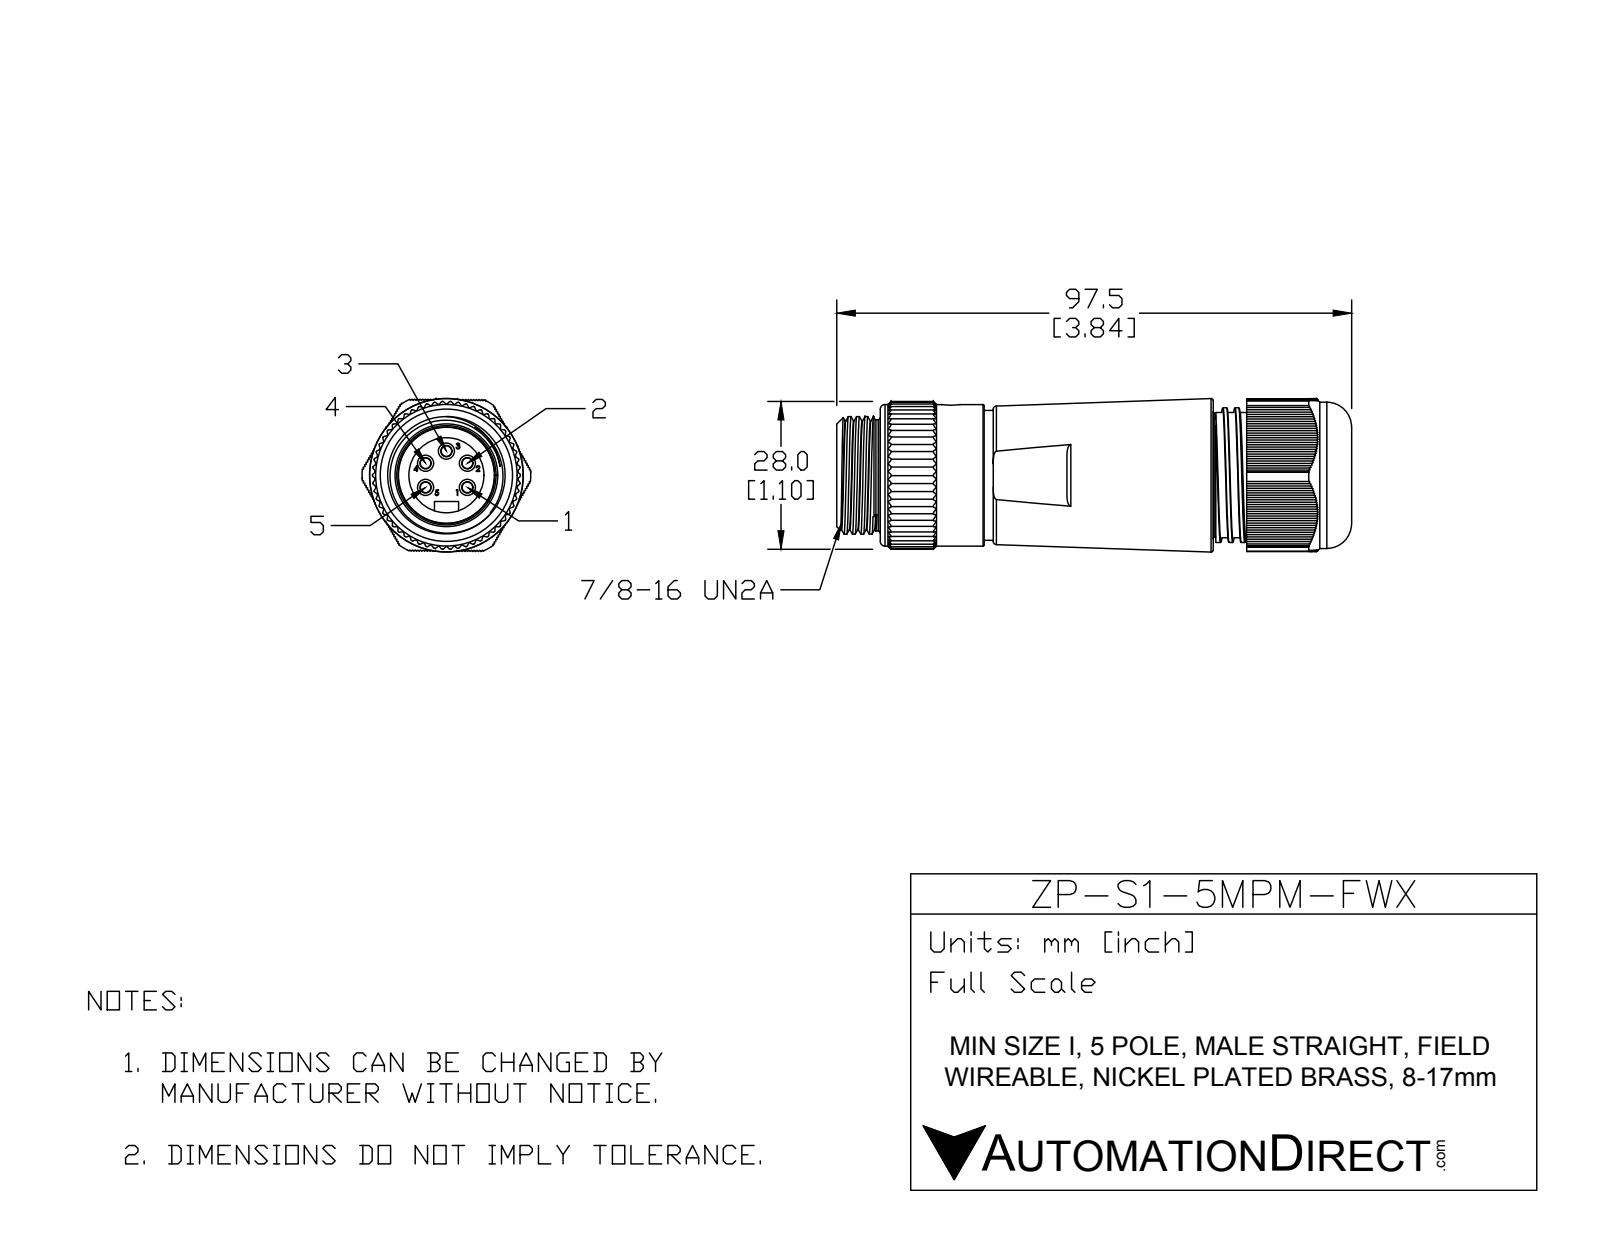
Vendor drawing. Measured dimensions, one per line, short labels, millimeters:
name: ZP-S1-5MPM-FWX
written by: SolidWorks 2015 (AUTOMOTIVE_DESIGN)
unit: mm
bodies: 9 solids, 937 faces (528 planar, 324 cylindrical, 85 other)
size: 97.56 × 31.9 × 29.06
volume: 49 362 mm³; area: 17 907 mm²
holes: 1× ⌀3.56, 1× ⌀14.22, 1× ⌀17.27, 1× ⌀18.28, 1× ⌀21.57, 1× ⌀24.2, 1× ⌀25.4
bosses: 5× ⌀3.15, 5× ⌀2, 1× ⌀27.69, 1× ⌀26.8, 1× ⌀25.5, 1× ⌀24.3, 1× ⌀22.22, 1× ⌀18.14
rounds: 165× R0.25, 1× R2.29, 1× R14, 1× R15.95
face distances: 68.78, 1.06, 0.35, 0.71, 6.35, 69.78, 1.41, 2.12, 1.77, 8.79
